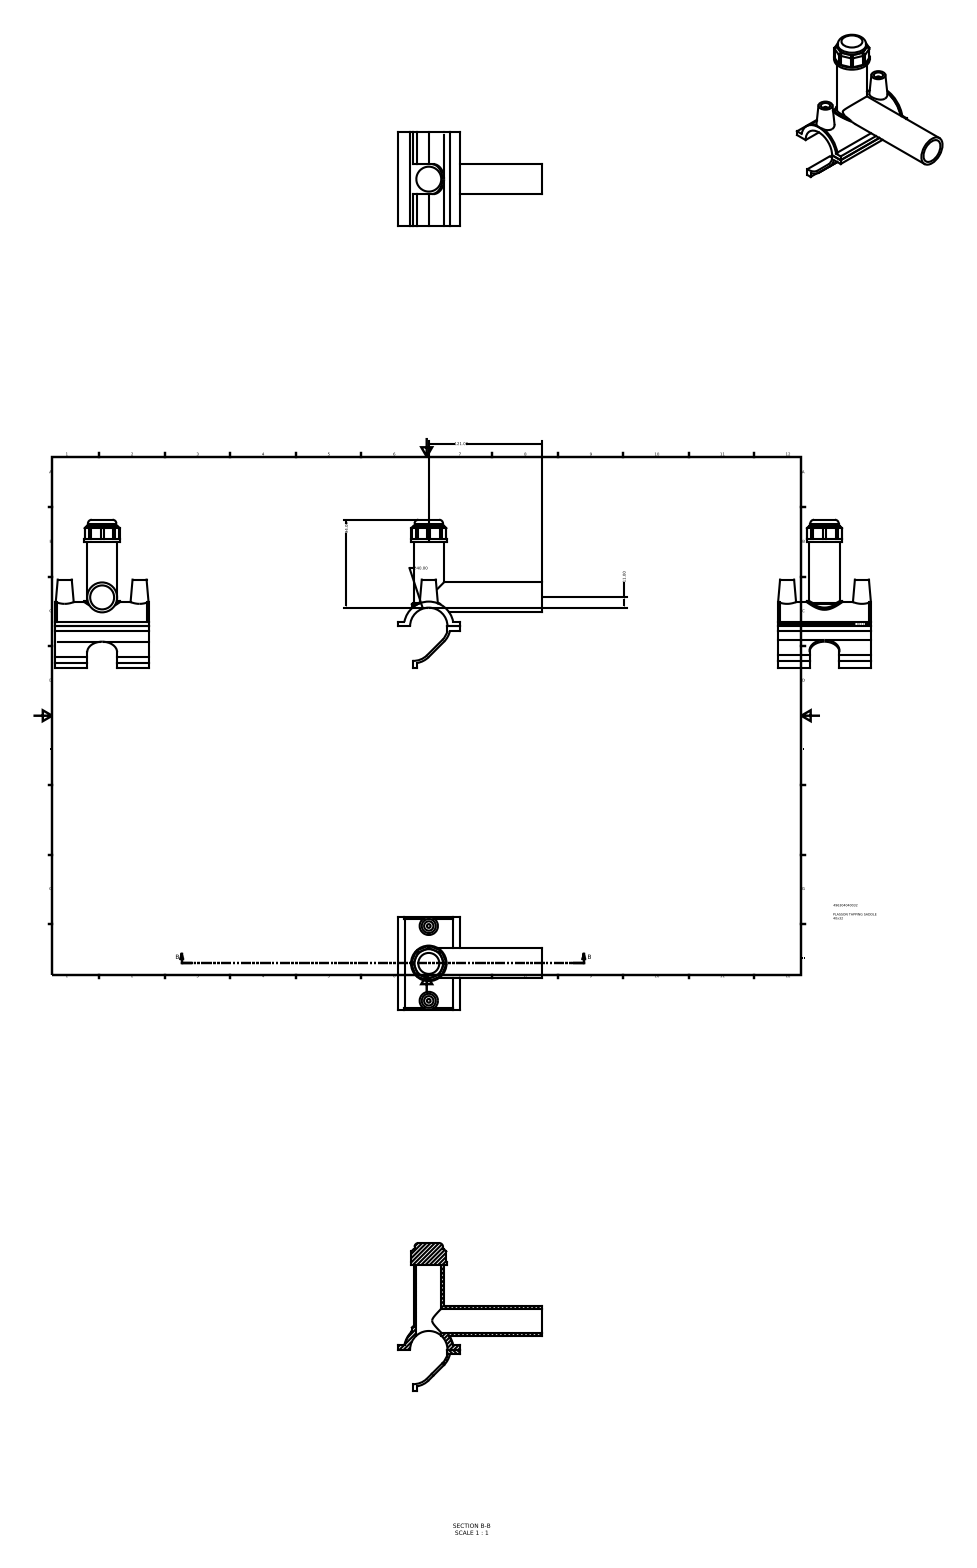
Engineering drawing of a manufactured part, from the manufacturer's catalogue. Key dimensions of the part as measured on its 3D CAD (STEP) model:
Part name (STEP PRODUCT): 496304040032
STEP written by: Autodesk Inventor 2015 (AUTOMOTIVE_DESIGN)
Units: millimetres
Bodies: 2 solids, 111 faces (66 planar, 32 cylindrical, 13 other)
Overall size (bounding box): 158.4 × 154 × 100
Volume: 144 498 mm³ · Surface area: 70 761 mm²
Round holes (diameter × count): ⌀10 ×2, ⌀25.6 ×1, ⌀26.6 ×1
Round bosses / shafts (diameter × count): ⌀4 ×2, ⌀38 ×1, ⌀32.3 ×1, ⌀32 ×1, ⌀30.4 ×1
Partial cylindrical surfaces — rounded edges, fillets, slot ends (radius × count): R4 ×8, R20.52 ×2, R23.12 ×2, R16 ×1, R18.05 ×1, R20 ×1, R26 ×1, R26.52 ×1
Main face-to-face distances: 4.95, 2.6, 9.9, 95.4, 90.45, 85.5, 100, 66, 35.12, 50.4
Hole centre spacings: 40, 80
